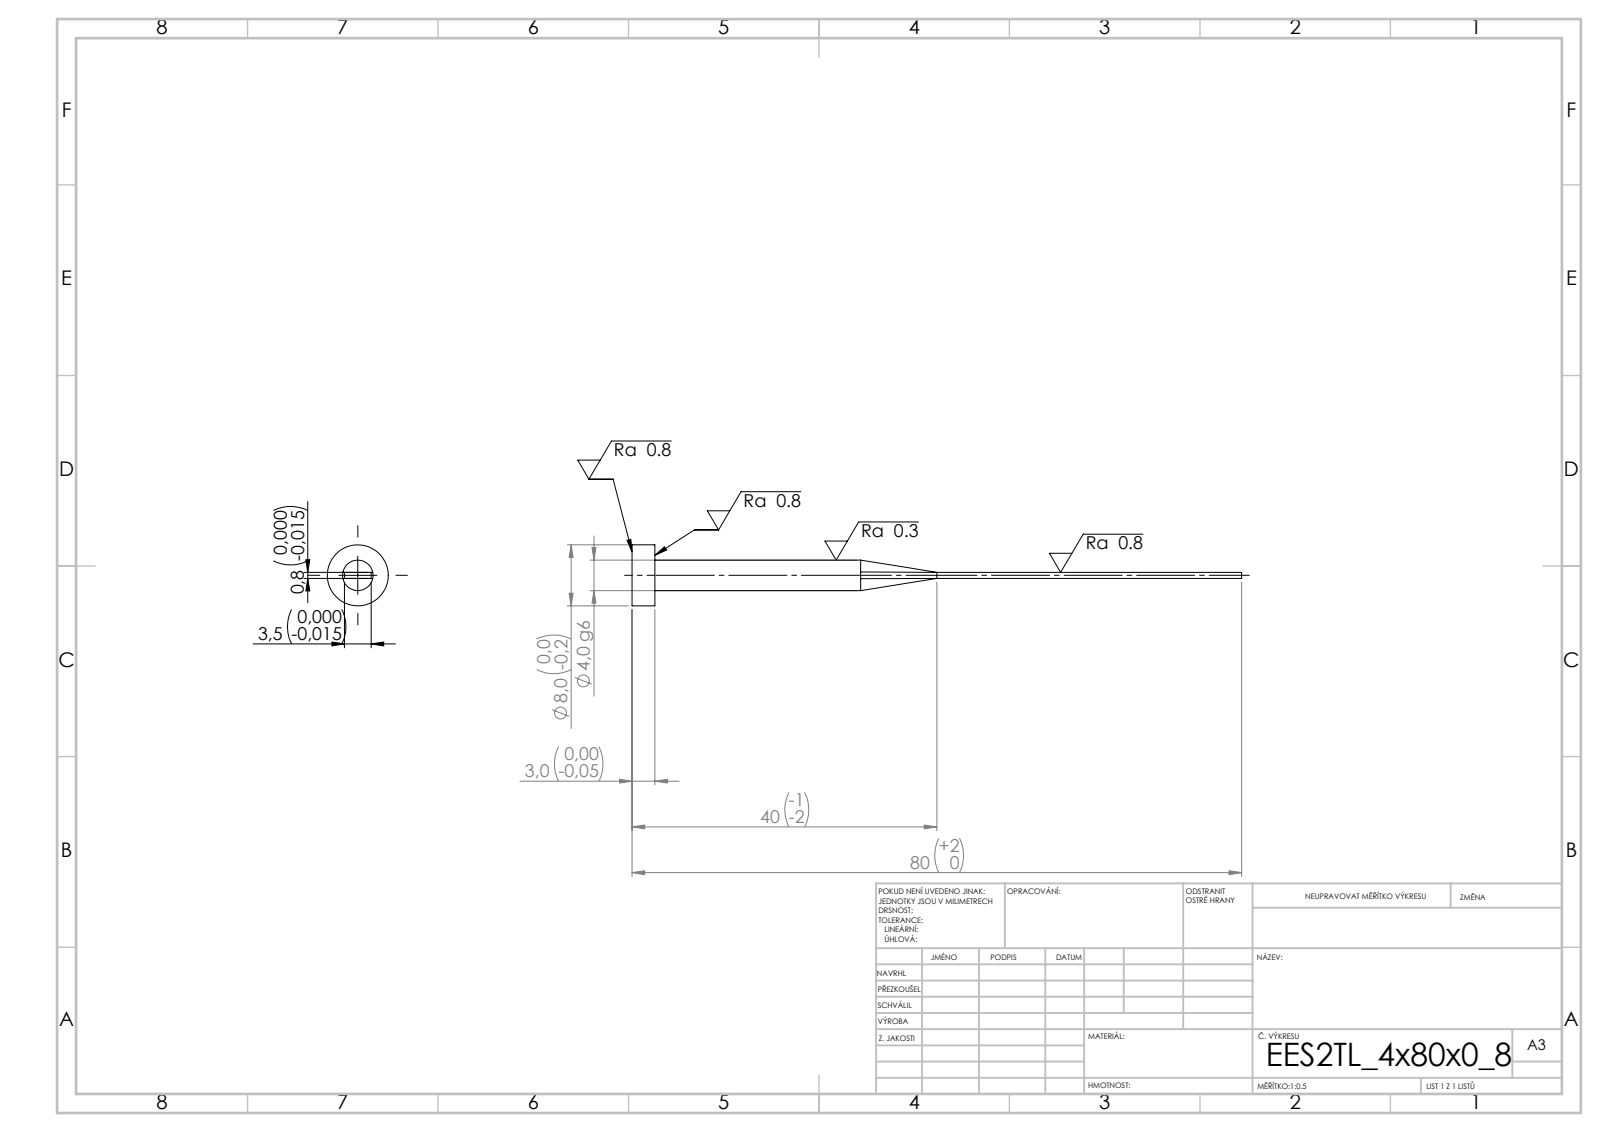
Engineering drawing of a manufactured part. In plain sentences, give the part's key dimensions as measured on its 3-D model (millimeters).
Its 3-D file was written by "SolidWorks 2019 (CONFIG_CONTROL_DESIGN)". It is 1 solid with 15 faces: 7 planar, 4 cylindrical and 4 other. Overall it measures 80 by 8 by 8 millimeters. Its volume is 675 cubic millimeters and its surface area 951 square millimeters. Round bosses or shafts: 1 of diameter 8, 1 of diameter 4. The main face-to-face distances are 0.8, 3, 3.5, 80, 77.
